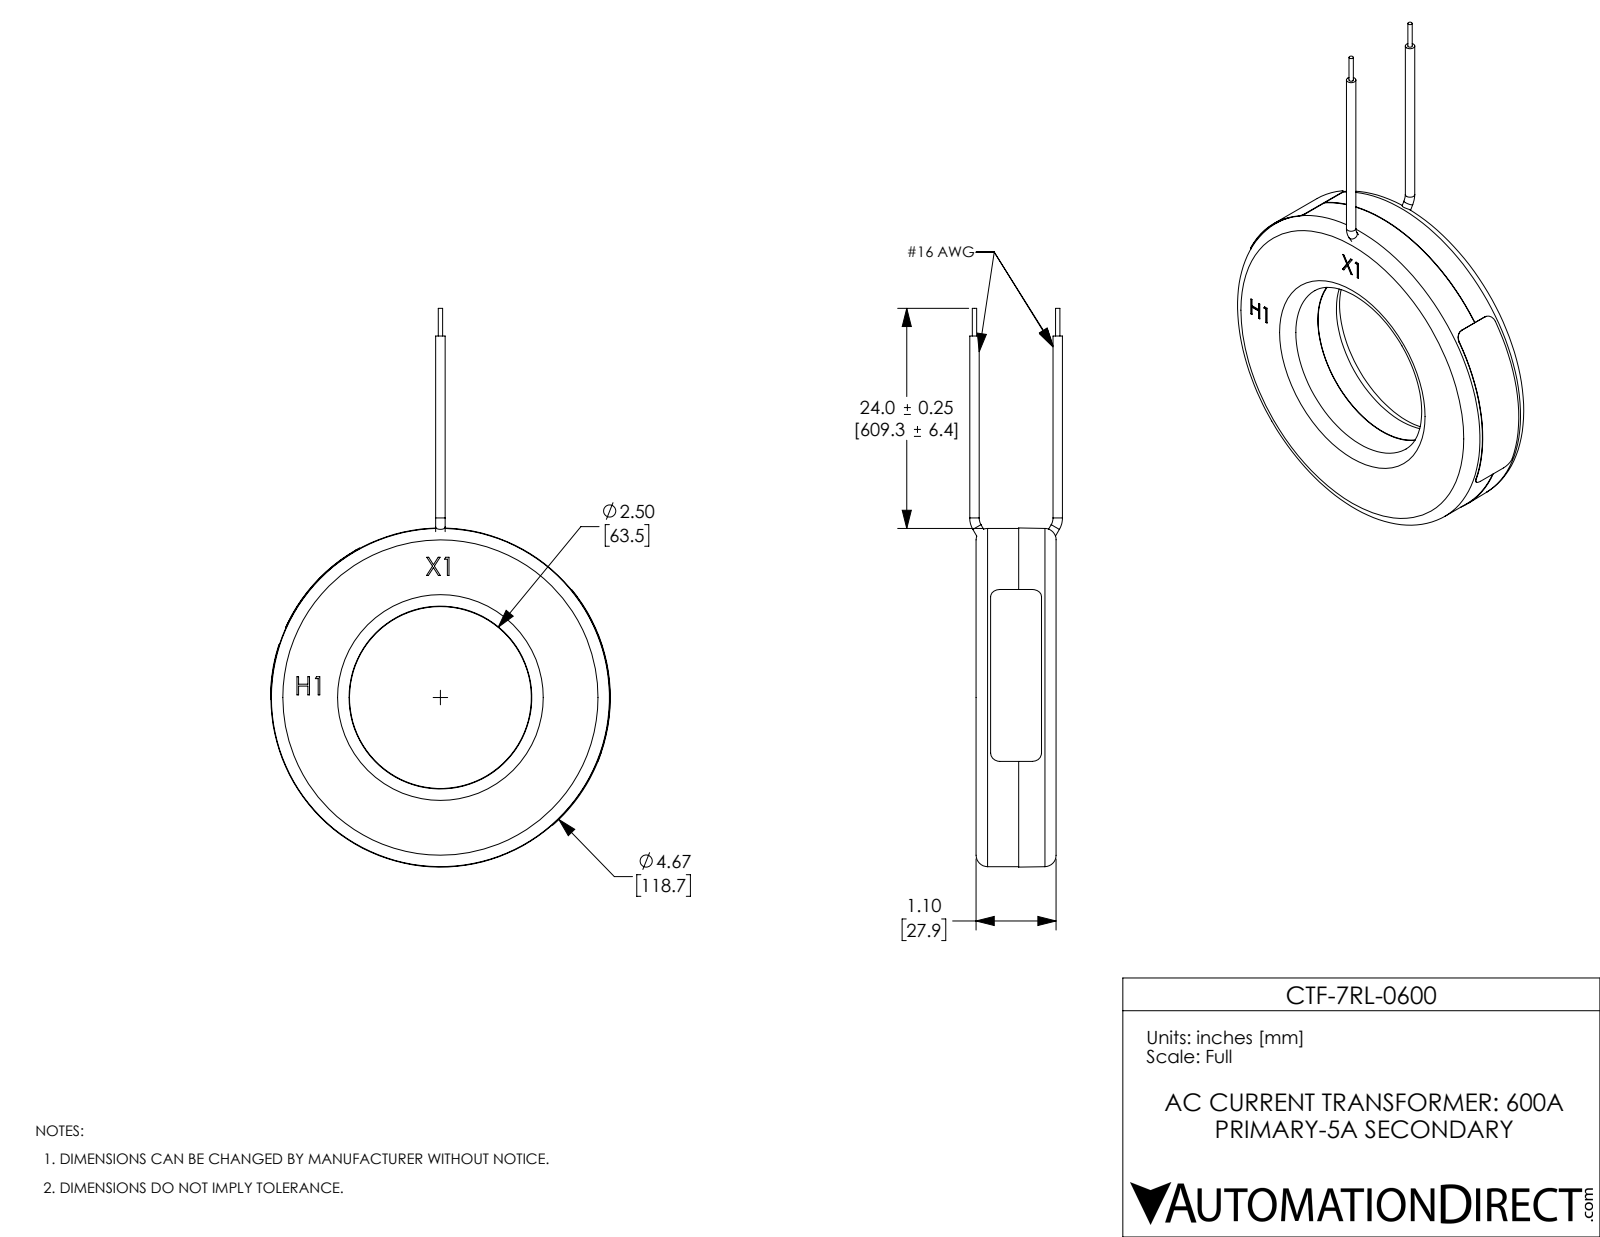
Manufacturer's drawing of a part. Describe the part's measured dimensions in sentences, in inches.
The part is named "CTF-7RL-0600". Its 3-D file was written by "SolidWorks 2018 (AUTOMOTIVE_DESIGN)". It is 6 solids with 114 faces: 62 planar, 31 cylindrical and 21 other. Overall it measures 7.679 by 4.673 by 1.275 inches. Its volume is 13.1 cubic inches and its surface area 79.58 square inches. Round holes: 1 of diameter 2.513. Round bosses or shafts: 4 of diameter 0.13, 2 of diameter 0.06, 1 of diameter 4.648. Partial cylindrical surfaces (rounded edges, fillets, slot ends): 4 of radius 0.06, 4 of radius 0.125, 1 of radius 2.33, 1 of radius 2.33, 1 of radius 2.331, 1 of radius 2.336. The main face-to-face distances are 0.515, 1.1, 0.585, 1.09, 0.575, 0.2, 0.9, 0.315, 0.89, 0.7.
